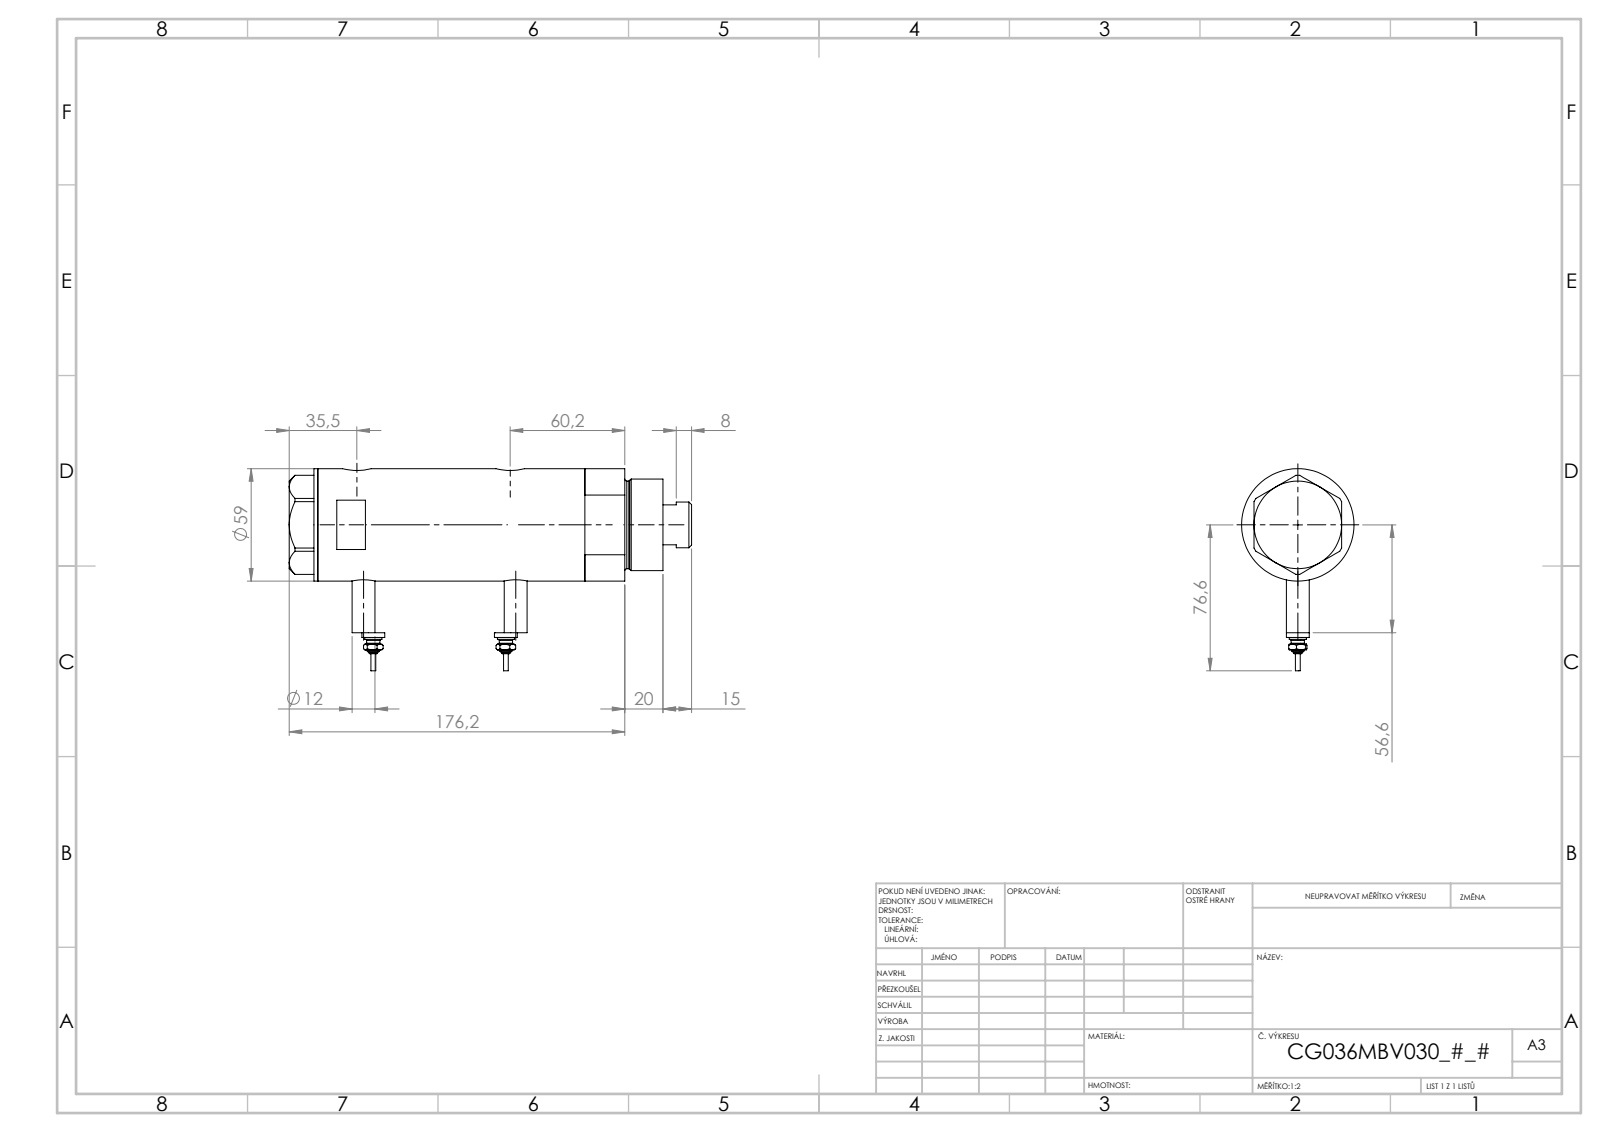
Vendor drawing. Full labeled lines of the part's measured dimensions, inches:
Part name (STEP PRODUCT): V270CG_BACK; V270CG_FRONT; V270CG_SWITCH; V270CG_VC (+1 more)
STEP written by: SolidWorks 2019 (CONFIG_CONTROL_DESIGN)
Units: inches
Bodies: 6 solids, 232 faces (81 planar, 77 cylindrical, 74 other)
Overall size (bounding box): 7.615 × 3.594 × 2.323
Volume: 26.86 in³ · Surface area: 147.5 in²
Round holes (diameter × count): ⌀0.197 ×2, ⌀0.383 ×2, ⌀0.492 ×2, ⌀0.591 ×2, ⌀0.335 ×1, ⌀0.984 ×1, ⌀1.043 ×1, ⌀1.417 ×1, ⌀1.575 ×1, ⌀2.047 ×1
Round bosses / shafts (diameter × count): ⌀0.472 ×3, ⌀0.354 ×2, ⌀0.276 ×2, ⌀0.171 ×2, ⌀0.094 ×2, ⌀2.323 ×1, ⌀1.89 ×1, ⌀1.811 ×1
Main face-to-face distances: 3.439, 0.925, 2.513, 0.591, 1.516, 4.029, 7.024, 6.434, 5.509, 2.995
Hole centre spacings: 0.114, 0.138, 2.447, 2.561, 2.585, 2.699, 0.114, 0.115
